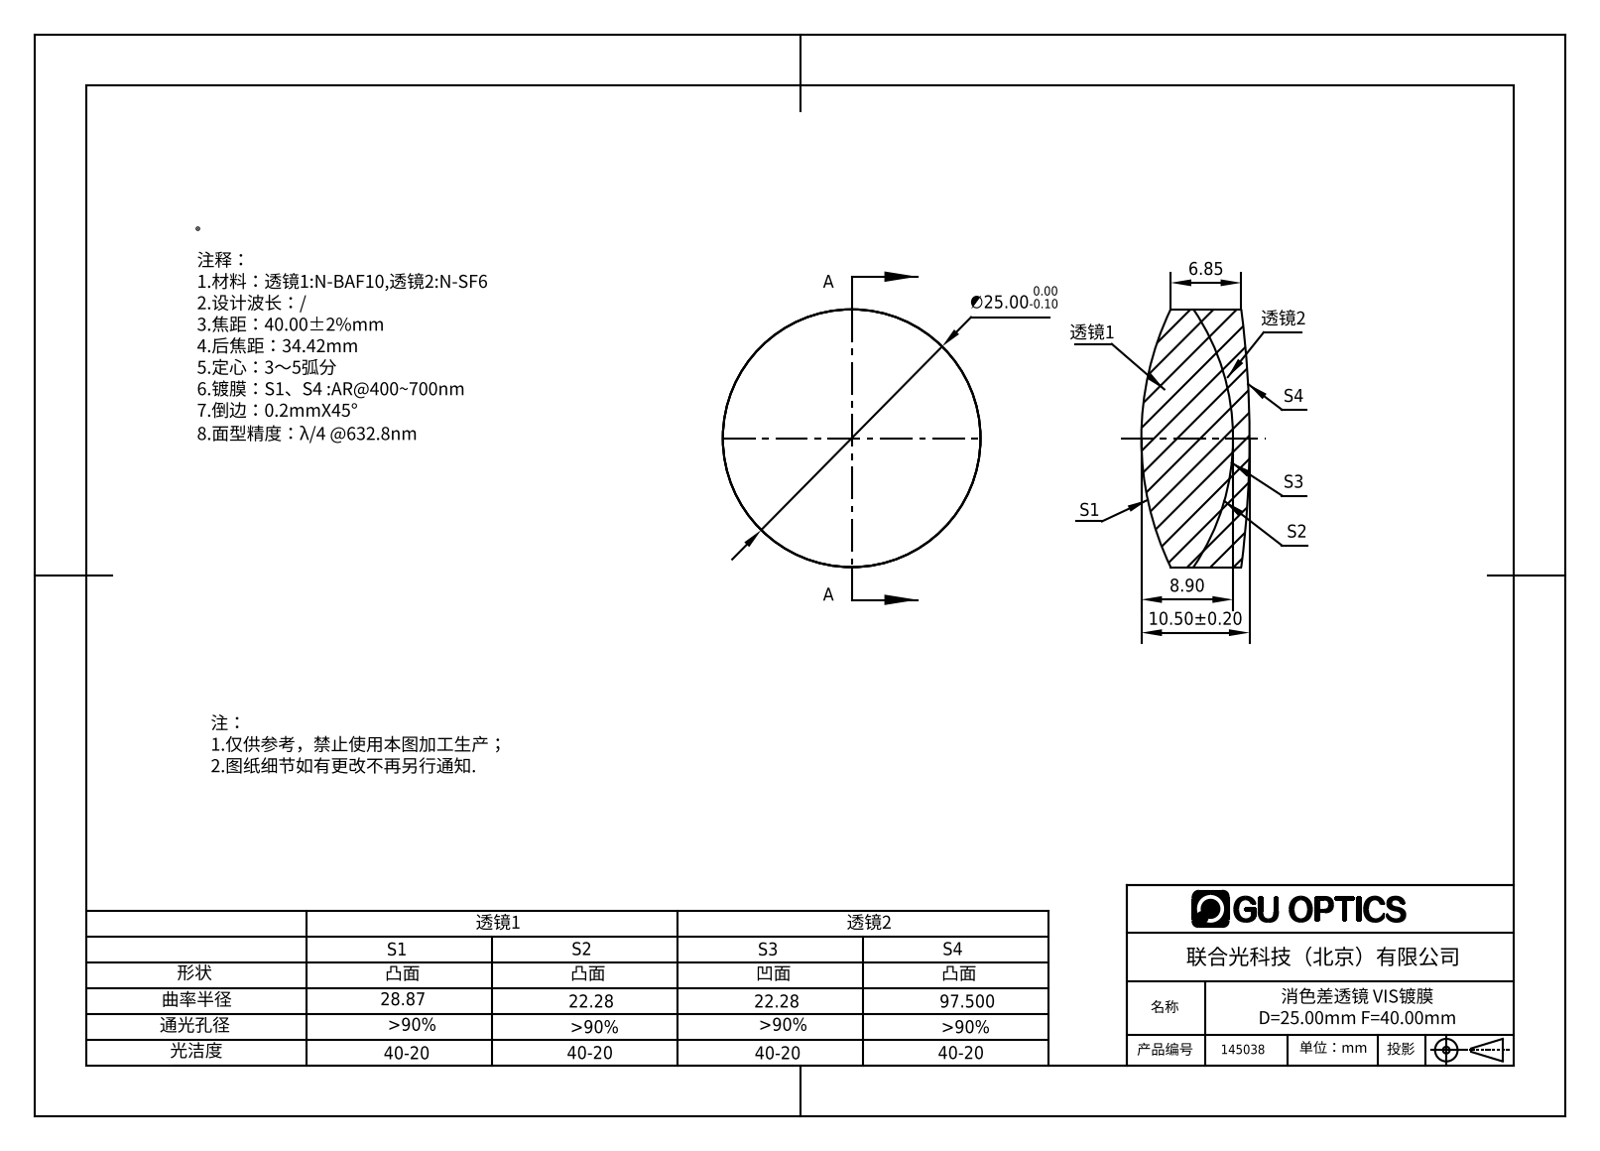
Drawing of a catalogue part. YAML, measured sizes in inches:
part_name: "145038"
step_written_by: "SolidWorks 2016 (AUTOMOTIVE_DESIGN)"
units: inches
bodies: {solids: 2, faces: 12, planar: 0, cylindrical: 4, other: 8}
overall_size: [0.984, 0.984, 0.413]
volume: 0.261
surface_area: 4.063
round_bosses_or_shafts:
  - {diameter: 0.984, count: 1}
